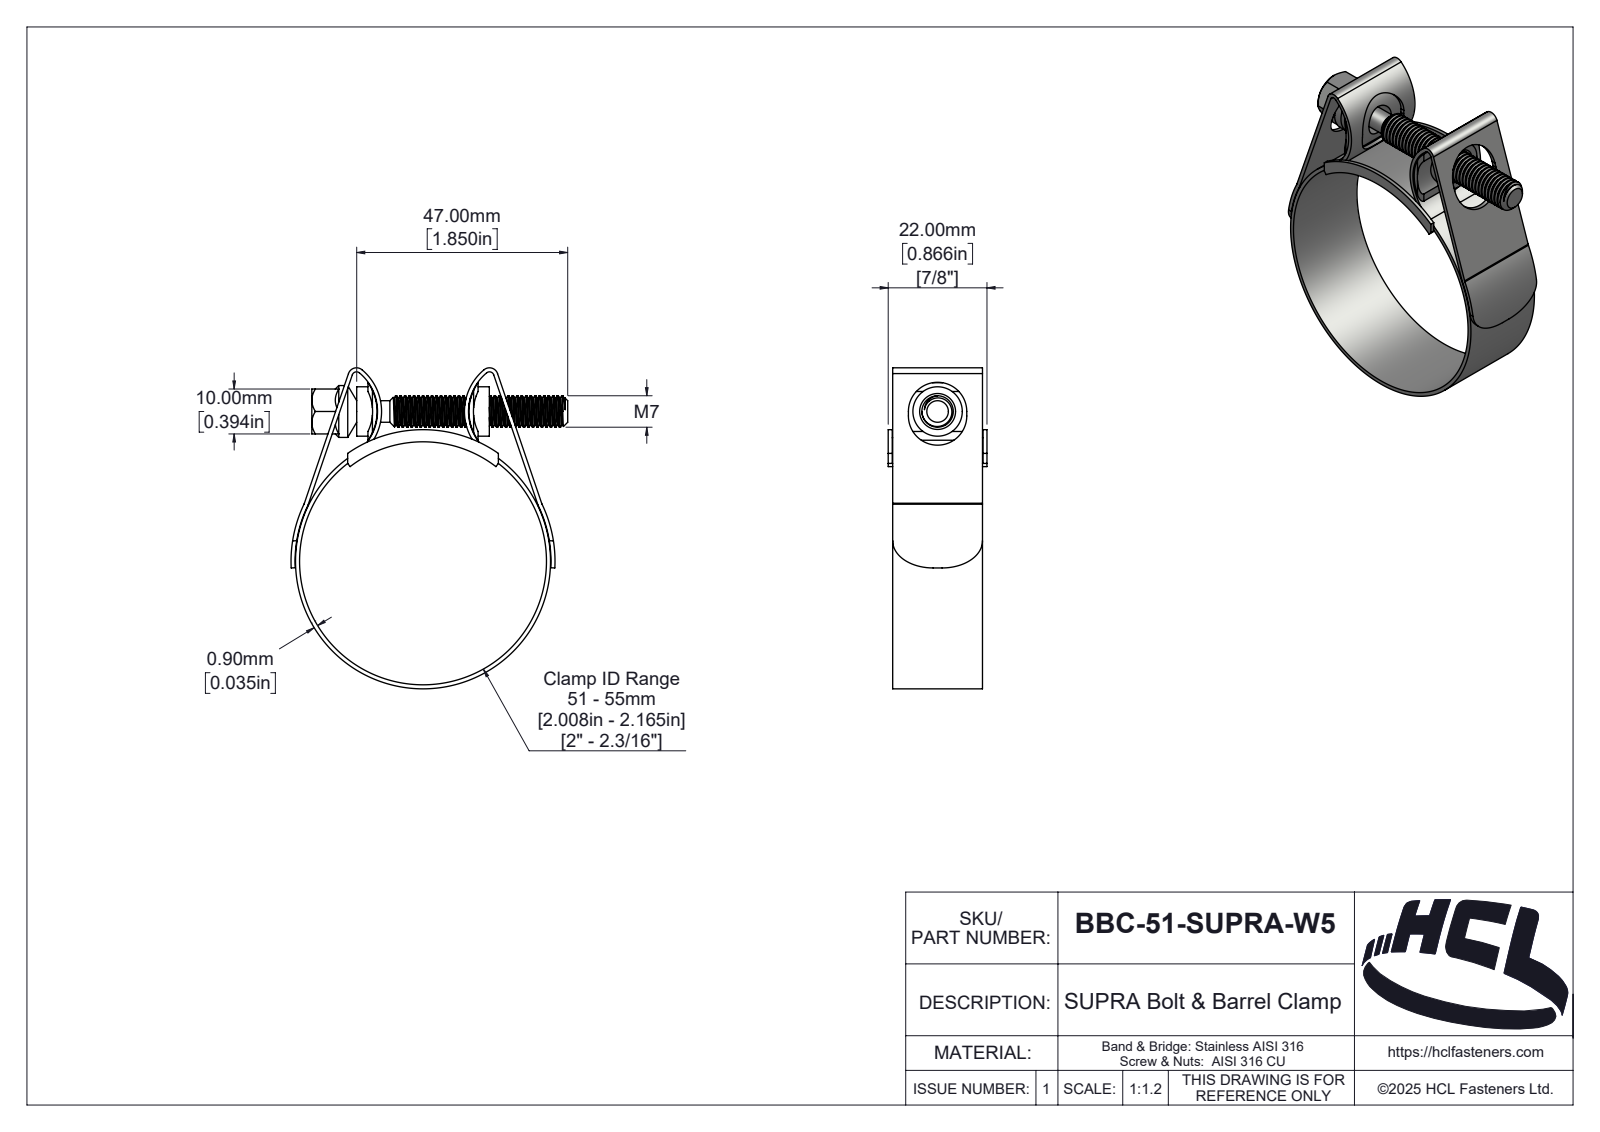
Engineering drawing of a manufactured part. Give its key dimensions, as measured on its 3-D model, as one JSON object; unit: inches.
{"part_name": "BBC-51-SUPRA-W5", "step_written_by": "SolidWorks 2025 (AUTOMOTIVE_DESIGN)", "units": "inches", "bodies": {"solids": 5, "faces": 319, "planar": 46, "cylindrical": 193, "other": 80}, "overall_size": [2.814, 2.426, 0.866], "volume_in3": 0.508, "surface_area_in2": 24.57, "round_holes": [[2.165, 1]], "round_bosses_or_shafts": [[2.236, 1], [0.455, 1], [0.433, 1], [0.276, 1], [0.189, 1]], "partial_cylinders_radius": [[0.039, 6], [0.075, 2], [0.079, 2], [0.114, 2], [0.256, 2], [0.396, 2], [0.436, 2], [0.44, 2]], "face_to_face_distances": [0.035, 0.787, 0.039, 0.827, 0.394, 0.831, 0.791, 0.866, 0.098, 1.065]}
